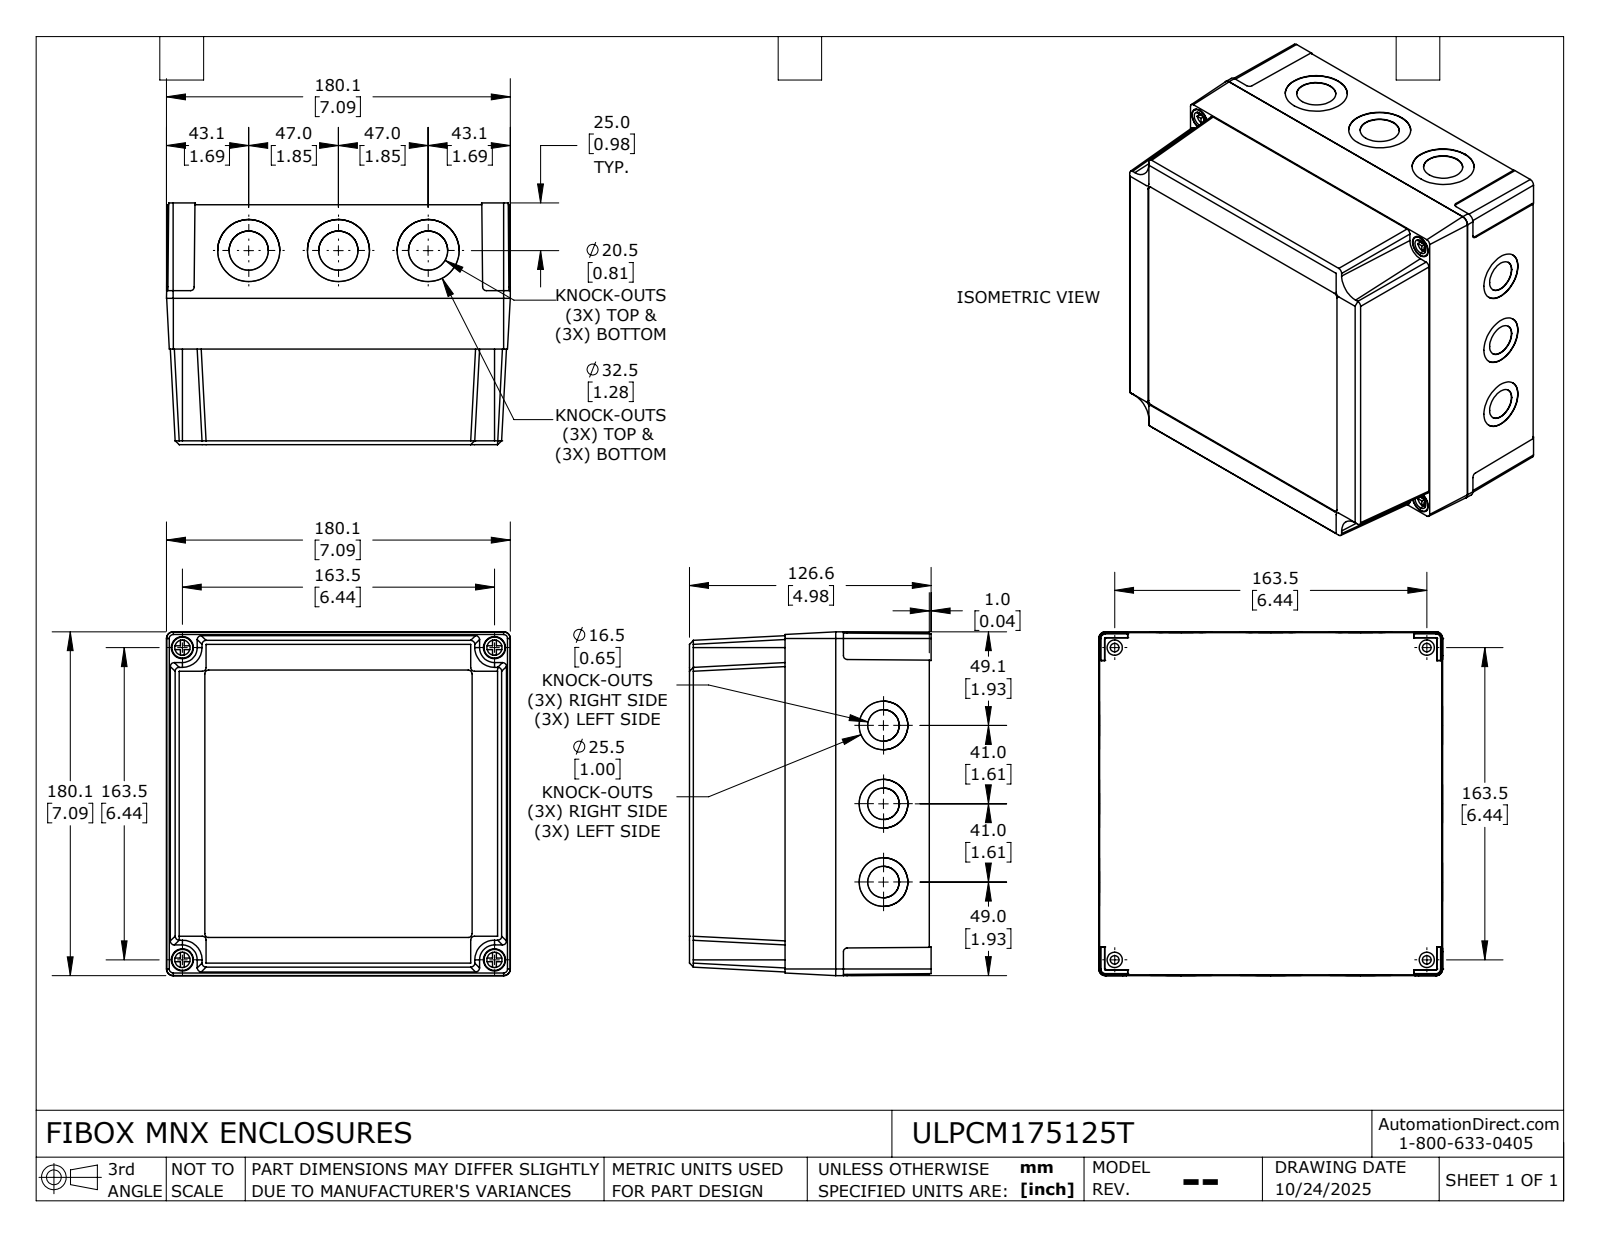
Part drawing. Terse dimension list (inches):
name: ULPCM175125T_Default
written by: SolidWorks 2024 (CONFIG_CONTROL_DESIGN)
unit: in
bodies: 6 solids, 629 faces (351 planar, 232 cylindrical, 46 other)
size: 7.091 × 7.091 × 4.984
volume: 26.97 in³; area: 479.7 in²
holes: 12× ⌀0.126, 12× ⌀0.157, 6× ⌀0.65, 6× ⌀0.807, 6× ⌀1.004, 6× ⌀1.28, 4× ⌀0.177, 4× ⌀0.315, 4× ⌀0.457
bosses: 12× ⌀0.315, 8× ⌀0.098, 4× ⌀0.433, 4× ⌀0.283
rounds: 8× R0.079, 8× R0.083, 6× R0.112, 4× R0.042, 4× R0.197, 2× R0.046
face distances: 0.118, 4.827, 4.709, 0.055, 0.165, 0.098, 4.925, 4.807, 0.077, 0.022
hole spacings: 1.333, 1.969, 2.866, 3.252, 4.79, 5.207, 5.469, 5.853
